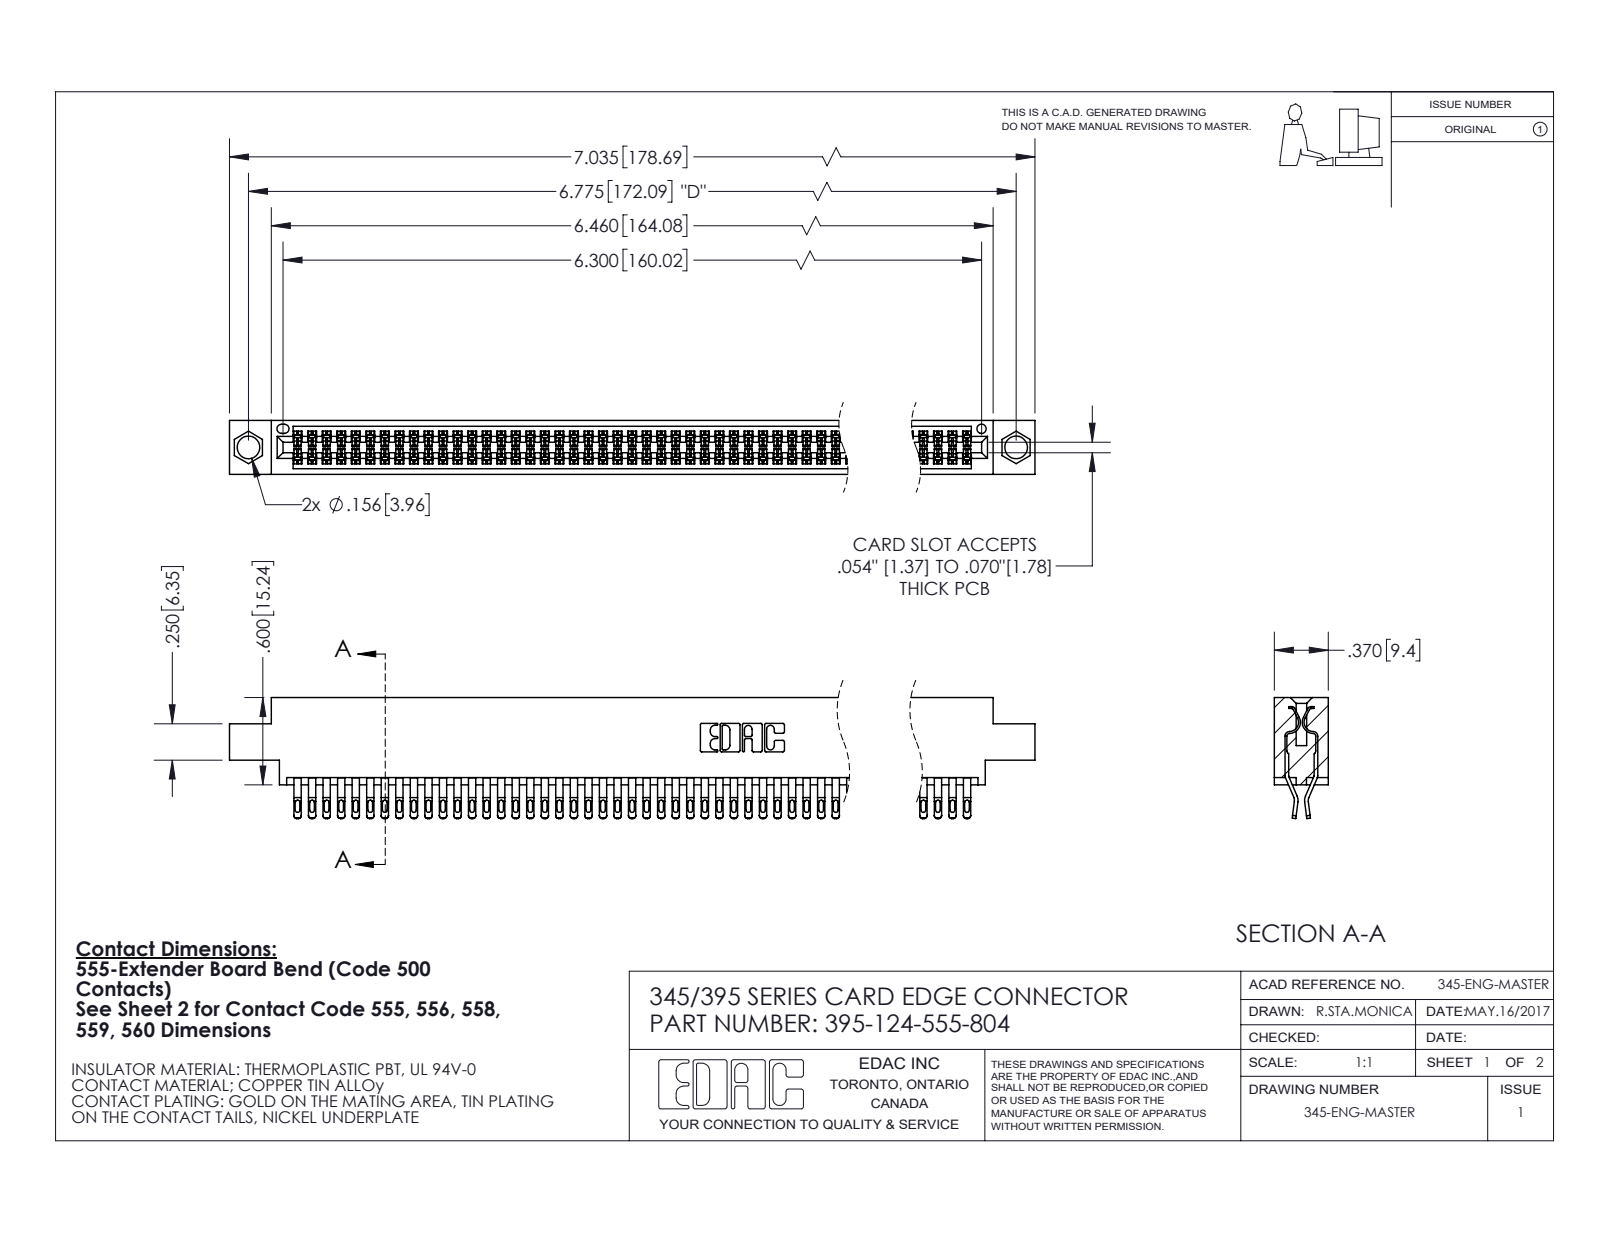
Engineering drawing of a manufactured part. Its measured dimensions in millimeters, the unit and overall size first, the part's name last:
Units: millimetres
Overall size (bounding box): 178.7 × 21.1 × 9.4
Round holes (diameter × count): ⌀4 ×2, ⌀1.6 ×1
Partial cylindrical surfaces — rounded edges, fillets, slot ends (radius × count): R0.4 ×310, R0.2 ×248, R0.5 ×248, R0.3 ×22, R0.2 ×6, R0.8 ×6, R0.7 ×3, R0.3 ×2
Main face-to-face distances: 1.8, 7.6, 0.6, 9.4, 5.1, 2.5, 6.9, 5.7, 4.4, 3.8
Hole centre spacings: 6.9, 166.1, 172.1
Volume: 17 680 mm³ · Surface area: 27 770 mm²
Bodies: 125 solids, 7088 faces (3942 planar, 3146 cylindrical, 0 other)
Part name (STEP PRODUCT): 345-292-001_555 Tail; 395-124-555-804; 345 Part_0.170 Offset - 0.156 Dia-TI
STEP written by: SolidWorks 2020 (CONFIG_CONTROL_DESIGN)
